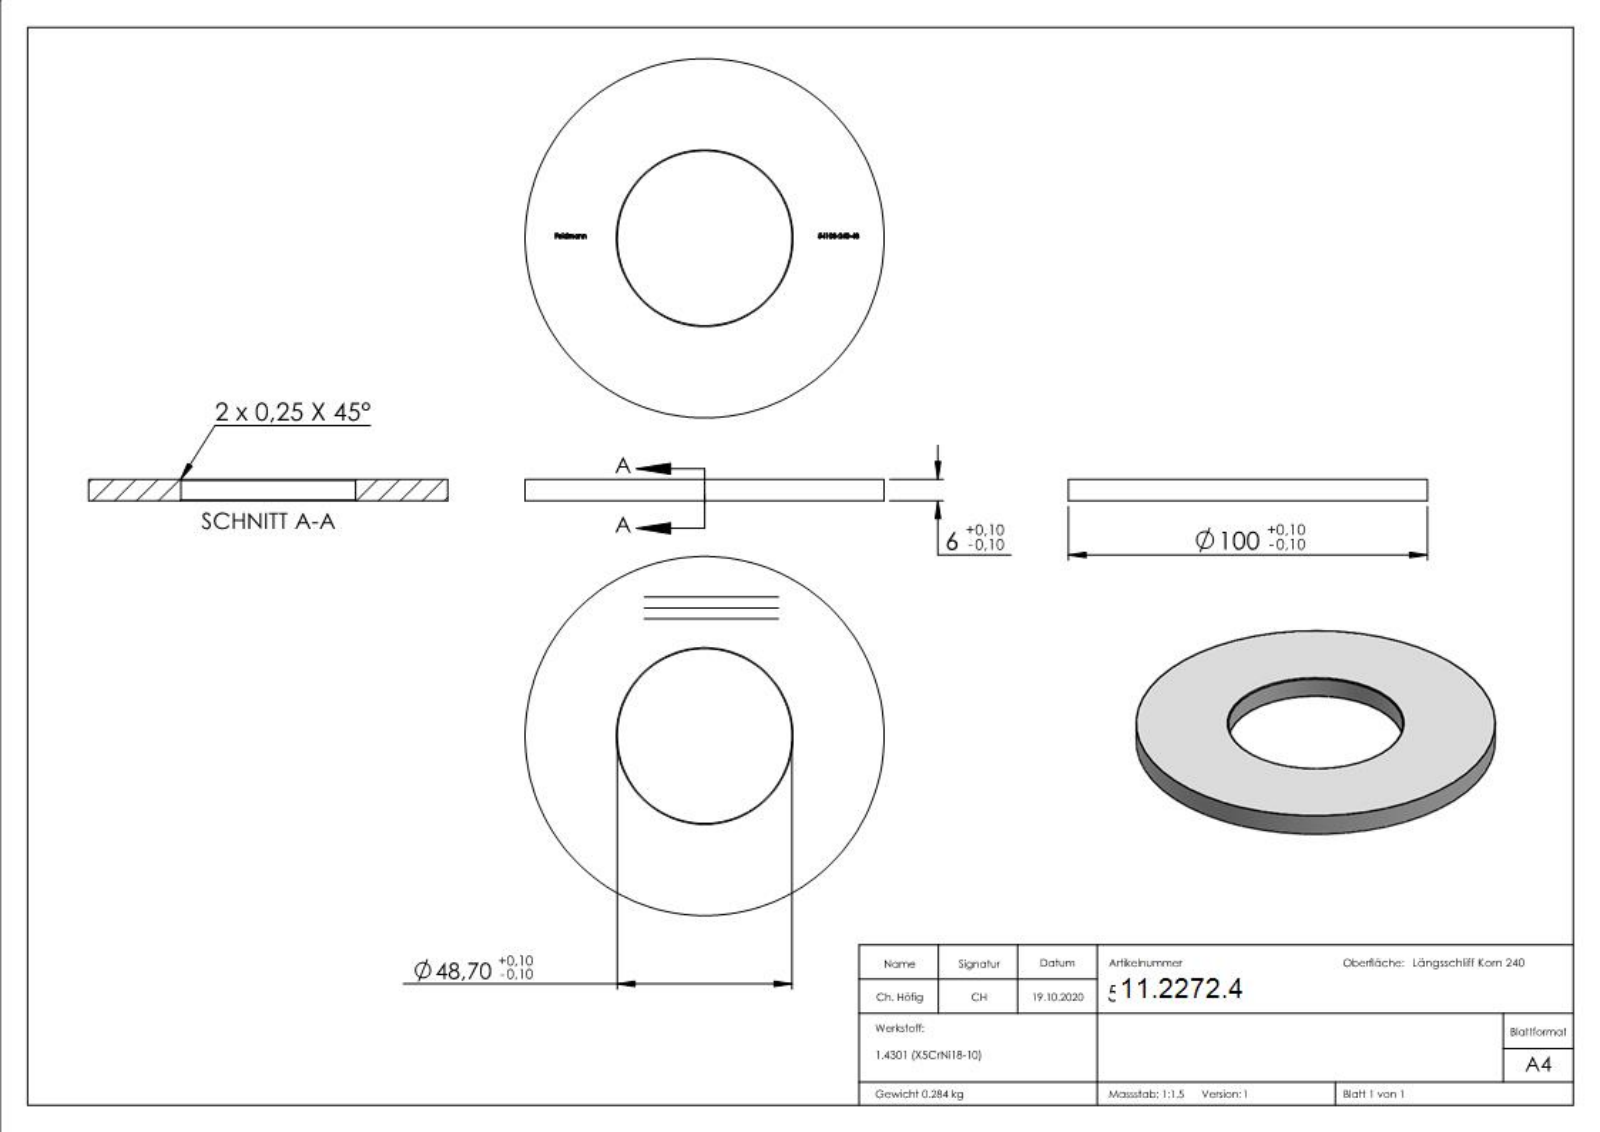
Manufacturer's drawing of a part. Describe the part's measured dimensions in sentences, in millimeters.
The part is named "54108-240-48". Its 3-D file was written by "SolidWorks 2018 (CONFIG_CONTROL_DESIGN)". It is 1 solid with 275 faces: 153 planar, 4 cylindrical and 118 other. Overall it measures 100 by 100 by 6 millimeters. Its volume is 35 937 cubic millimeters and its surface area 14 752 square millimeters. Round holes: 1 of diameter 48.7. Round bosses or shafts: 1 of diameter 100. The main face-to-face distances are 6, 5.9, 0.44, 0.88, 0.31, 75.67, 0.58, 0.39, 0.79, 8.34.
